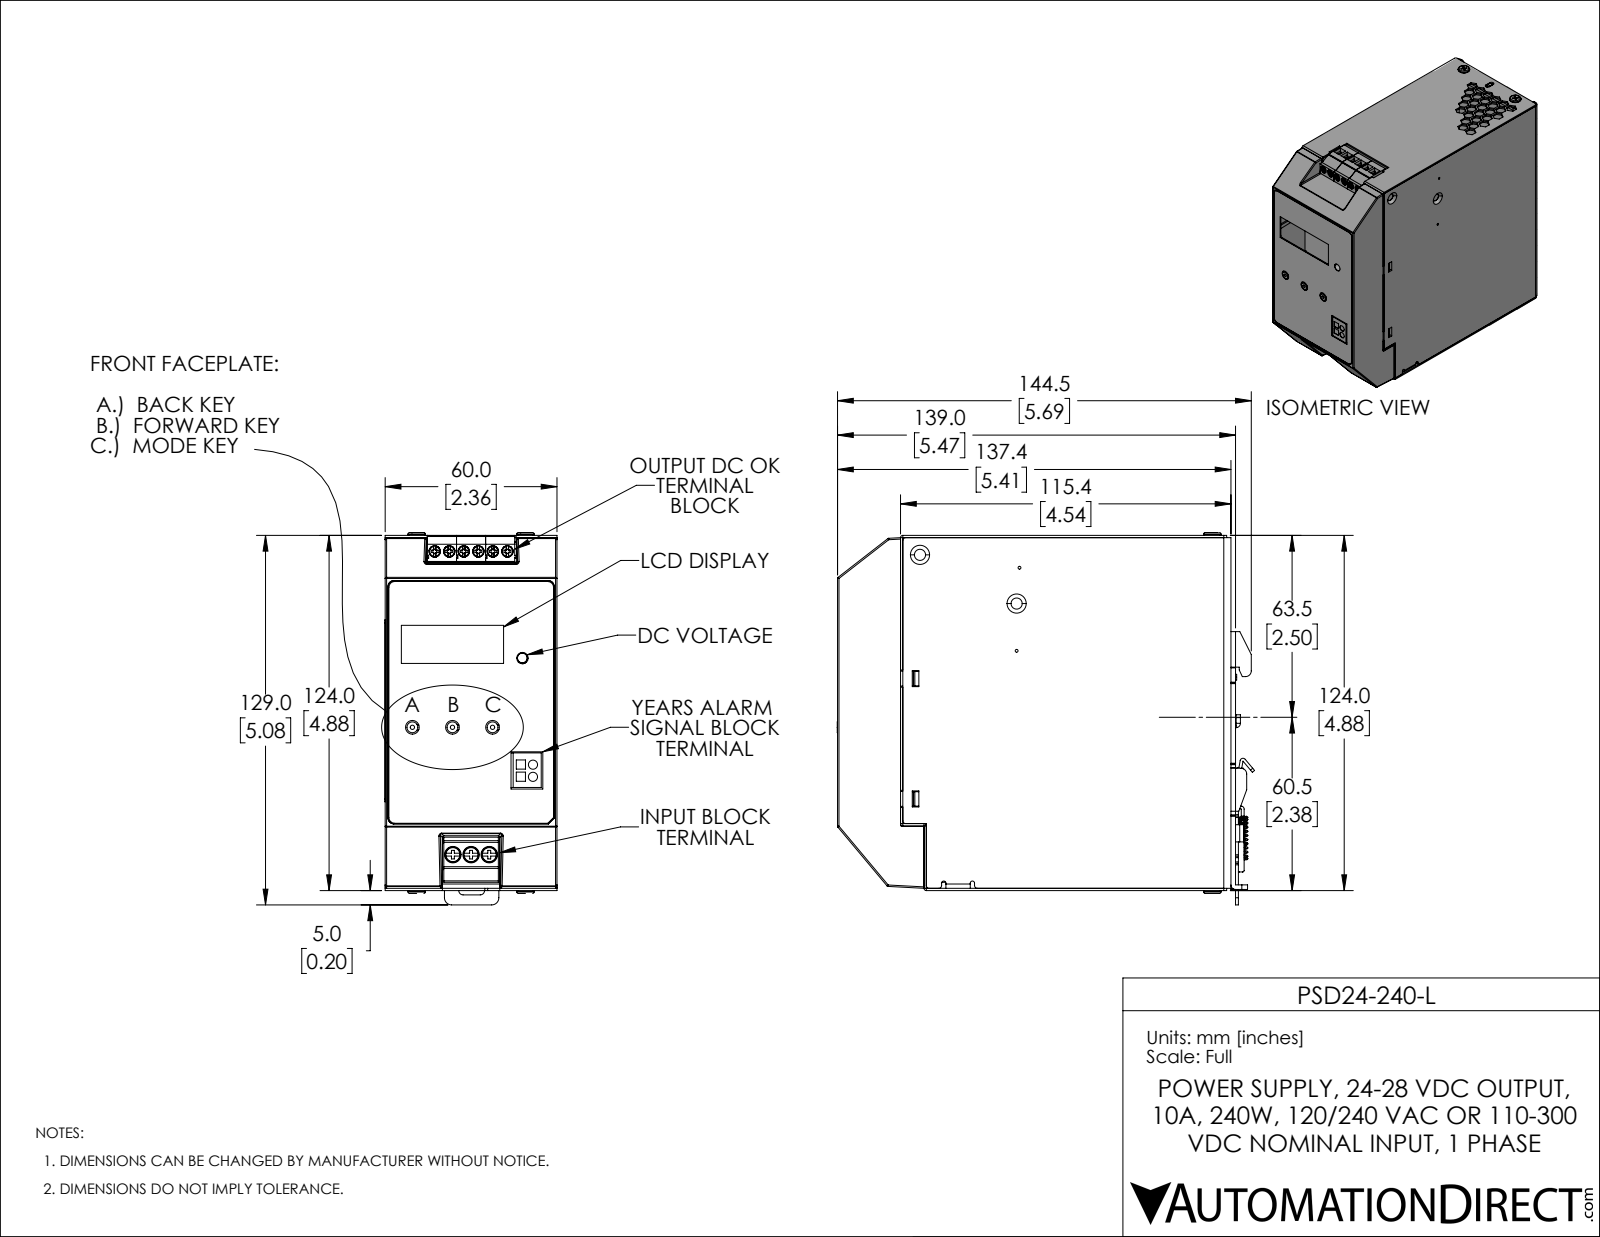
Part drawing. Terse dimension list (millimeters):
name: PSD24-240-L
written by: SolidWorks 2019 (AUTOMOTIVE_DESIGN)
unit: mm
bodies: 33 solids, 3129 faces (2287 planar, 504 cylindrical, 338 other)
size: 145.7 × 130 × 60.1
volume: 117 000 mm³; area: 179 400 mm²
holes: 8× ⌀4, 7× ⌀3.5, 6× ⌀3.9, 4× ⌀1, 4× ⌀2.5, 3× ⌀4.8, 3× ⌀4.9, 2× ⌀3.2, 1× ⌀3.7, 1× ⌀3.8
bosses: 6× ⌀3.9, 4× ⌀5.5, 4× ⌀2, 3× ⌀5.7, 3× ⌀3.5, 2× ⌀6, 2× ⌀2.9, 1× ⌀3.4
rounds: 75× R0.5, 60× R0.3, 47× R1, 24× R0.1, 22× R0.2, 16× R0.3, 11× R0.8, 6× R1.5
face distances: 1.5, 58.5, 0.8, 60, 57, 123.2, 137.1, 135.6, 122.4, 115.4
hole spacings: 5.1, 10.2, 15.2, 28, 34.9, 6.4, 9, 14
